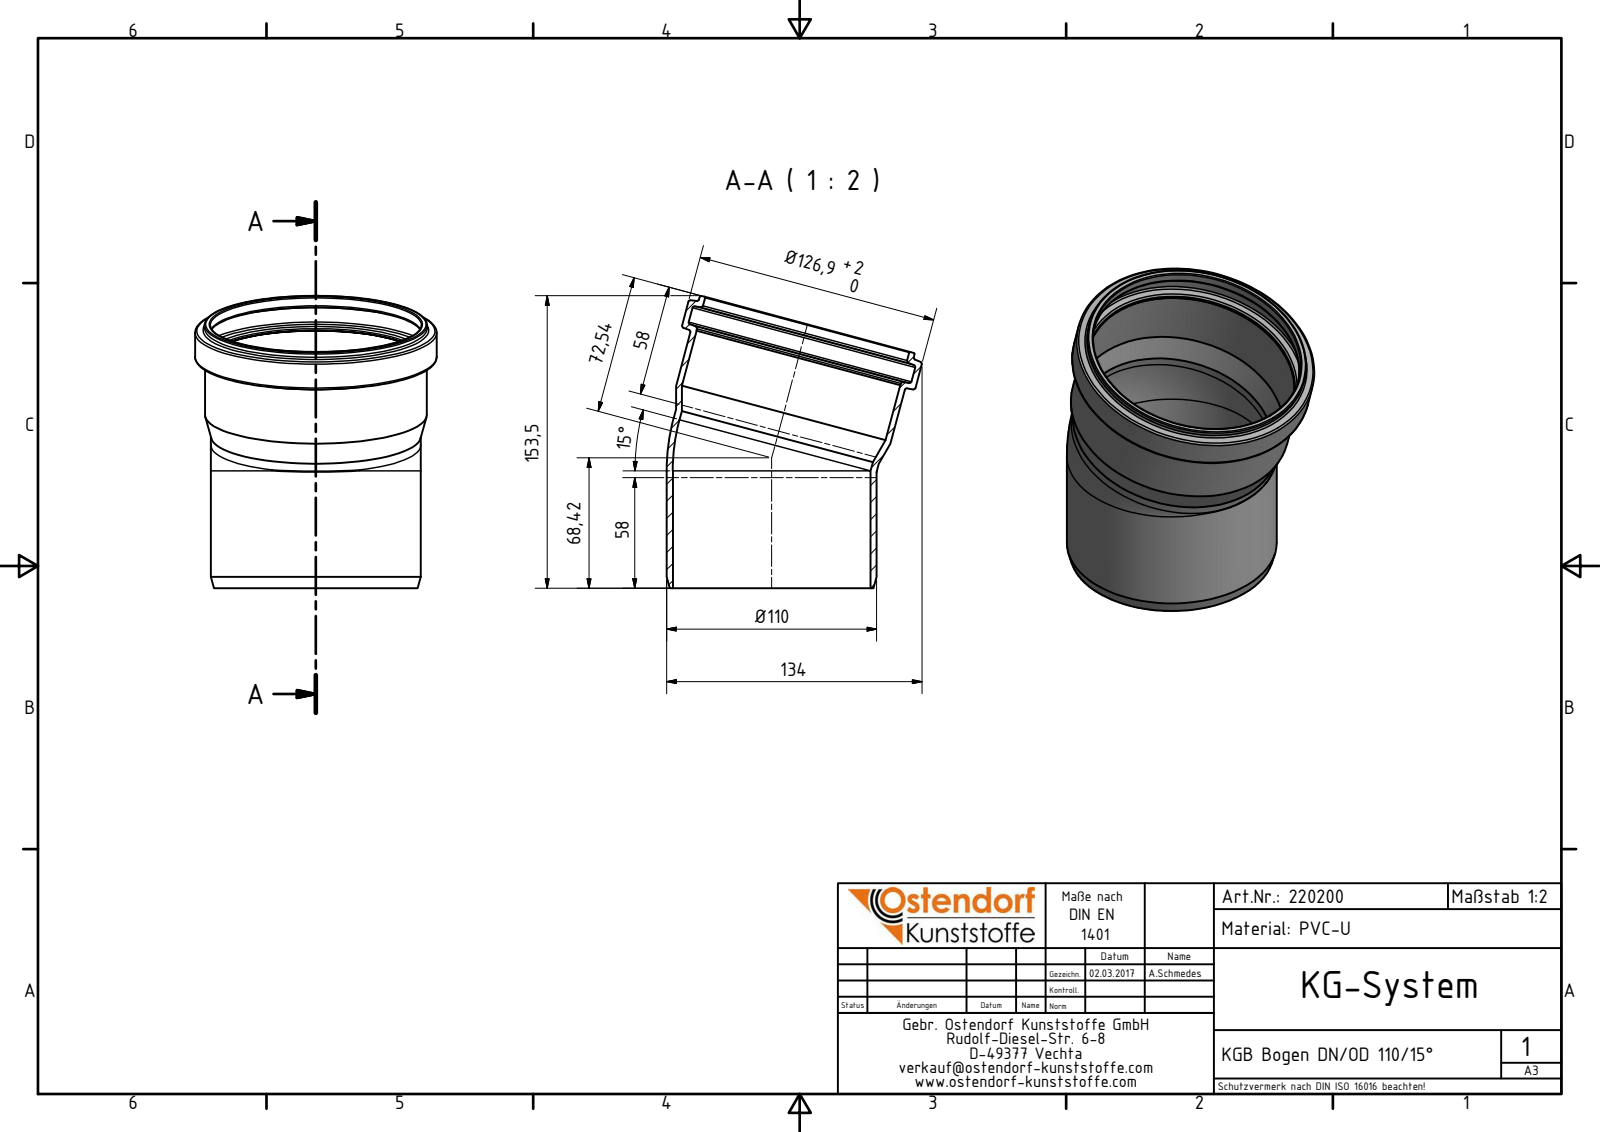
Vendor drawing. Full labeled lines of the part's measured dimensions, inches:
Part name (STEP PRODUCT): 220200 KGB Bogen DN_OD 110_15°
STEP written by: Autodesk Inventor 2016 (AUTOMOTIVE_DESIGN)
Units: inches
Bodies: 1 solid, 34 faces (3 planar, 11 cylindrical, 20 other)
Overall size (bounding box): 6.043 × 5.276 × 4.996
Volume: 9.634 in³ · Surface area: 163.5 in²
Round holes (diameter × count): ⌀4.087 ×2, ⌀4.358 ×1, ⌀4.37 ×1, ⌀4.768 ×1
Round bosses / shafts (diameter × count): ⌀4.339 ×2, ⌀4.996 ×1, ⌀4.598 ×1, ⌀4.587 ×1
Main face-to-face distances: 0.719
